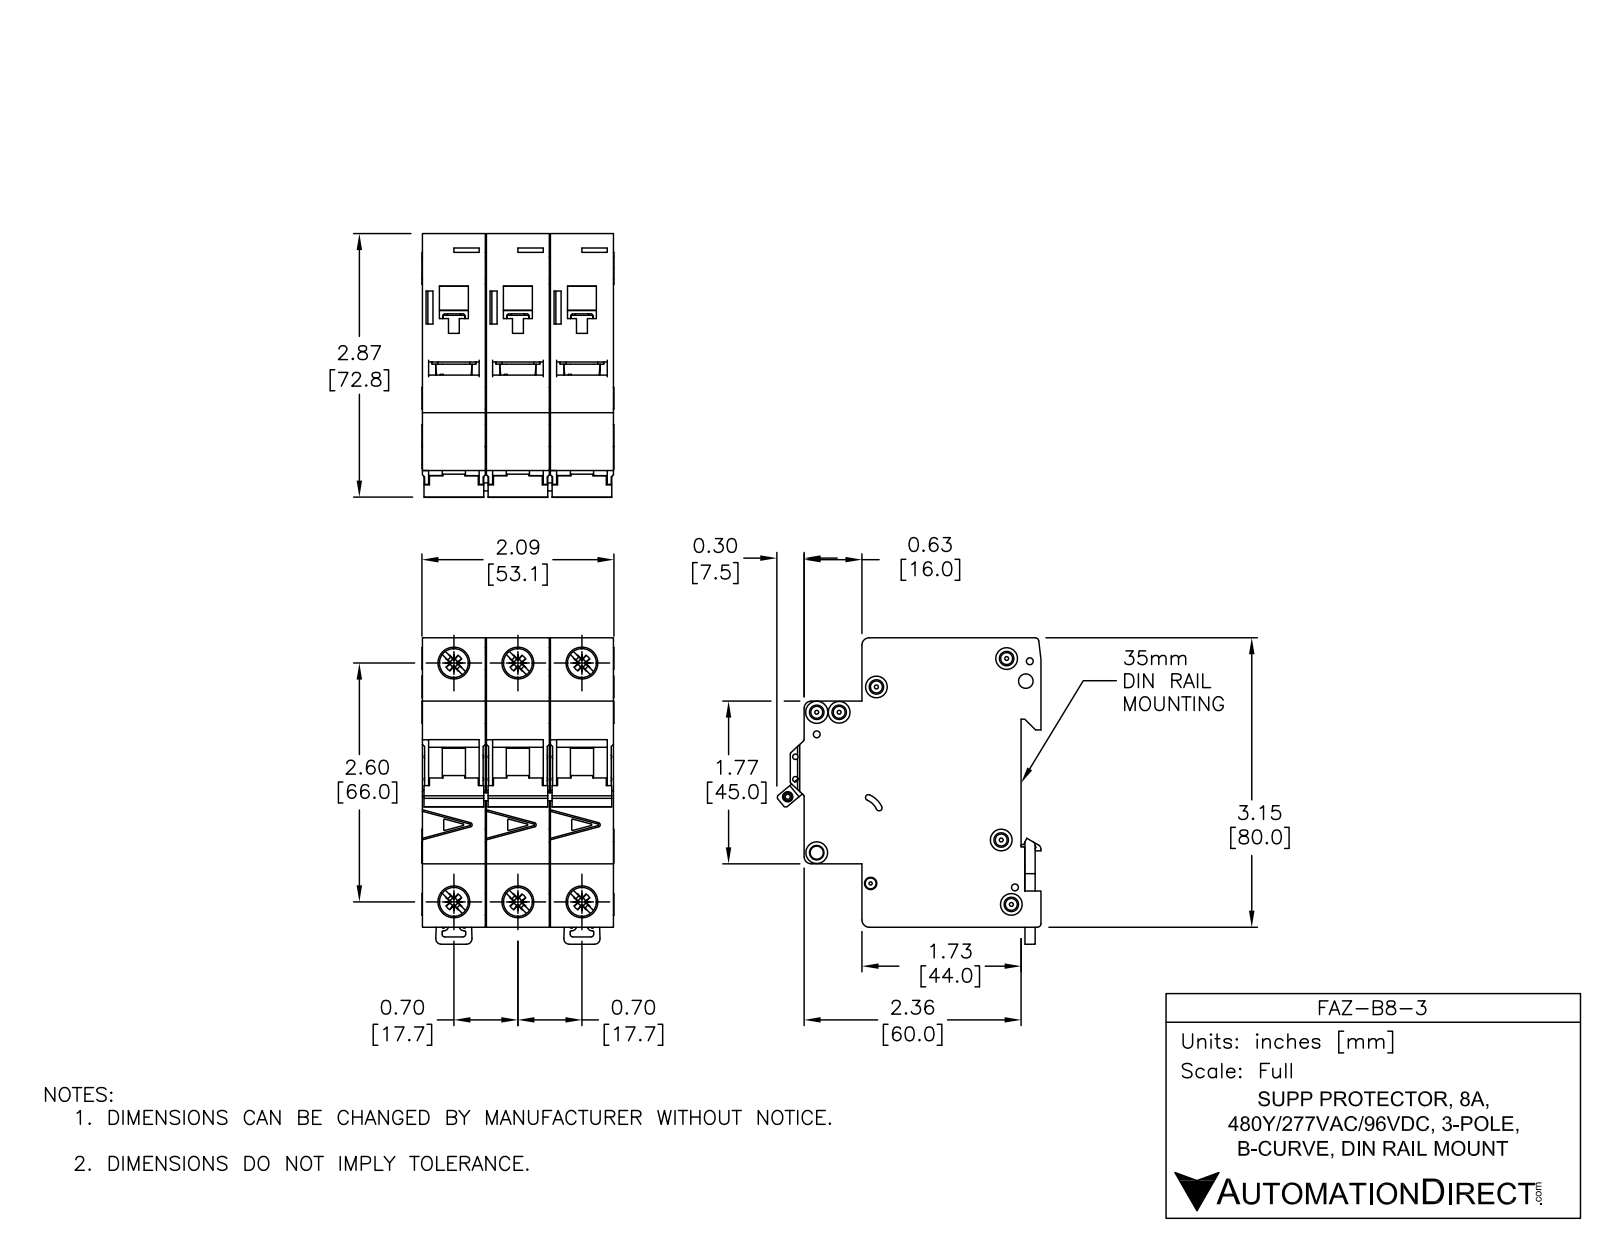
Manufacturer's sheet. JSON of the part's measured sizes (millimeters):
{"part_name": "FAZ-B8-3", "step_written_by": "SolidWorks 2014 (AUTOMOTIVE_DESIGN)", "units": "millimeters", "bodies": {"solids": 11, "faces": 1650, "planar": 697, "cylindrical": 590, "other": 363}, "overall_size": [84.78, 73.04, 53.1], "volume_mm3": 224680, "surface_area_mm2": 58052, "round_holes": [[3.6, 6], [8.2, 4], [1.9, 3], [1.09, 2], [1.5, 2], [4, 2], [7.15, 2], [2.15, 1], [2.2, 1], [2.55, 1], [3.3, 1], [3.4, 1]], "round_bosses_or_shafts": [[6, 4], [2.5, 3], [8.2, 2]], "partial_cylinders_radius": [[0.25, 68], [0.5, 25], [1, 12], [2, 12], [0.2, 11], [1.8, 3], [0.8, 2], [3, 2]], "face_to_face_distances": [17.7, 17.5, 35.4, 35.2, 52.9, 17.9, 79.48, 5.5, 49.5, 44], "hole_center_spacings": [17.7, 68.33, 66, 6.2, 13.64, 35.4, 74.89, 4.81]}
